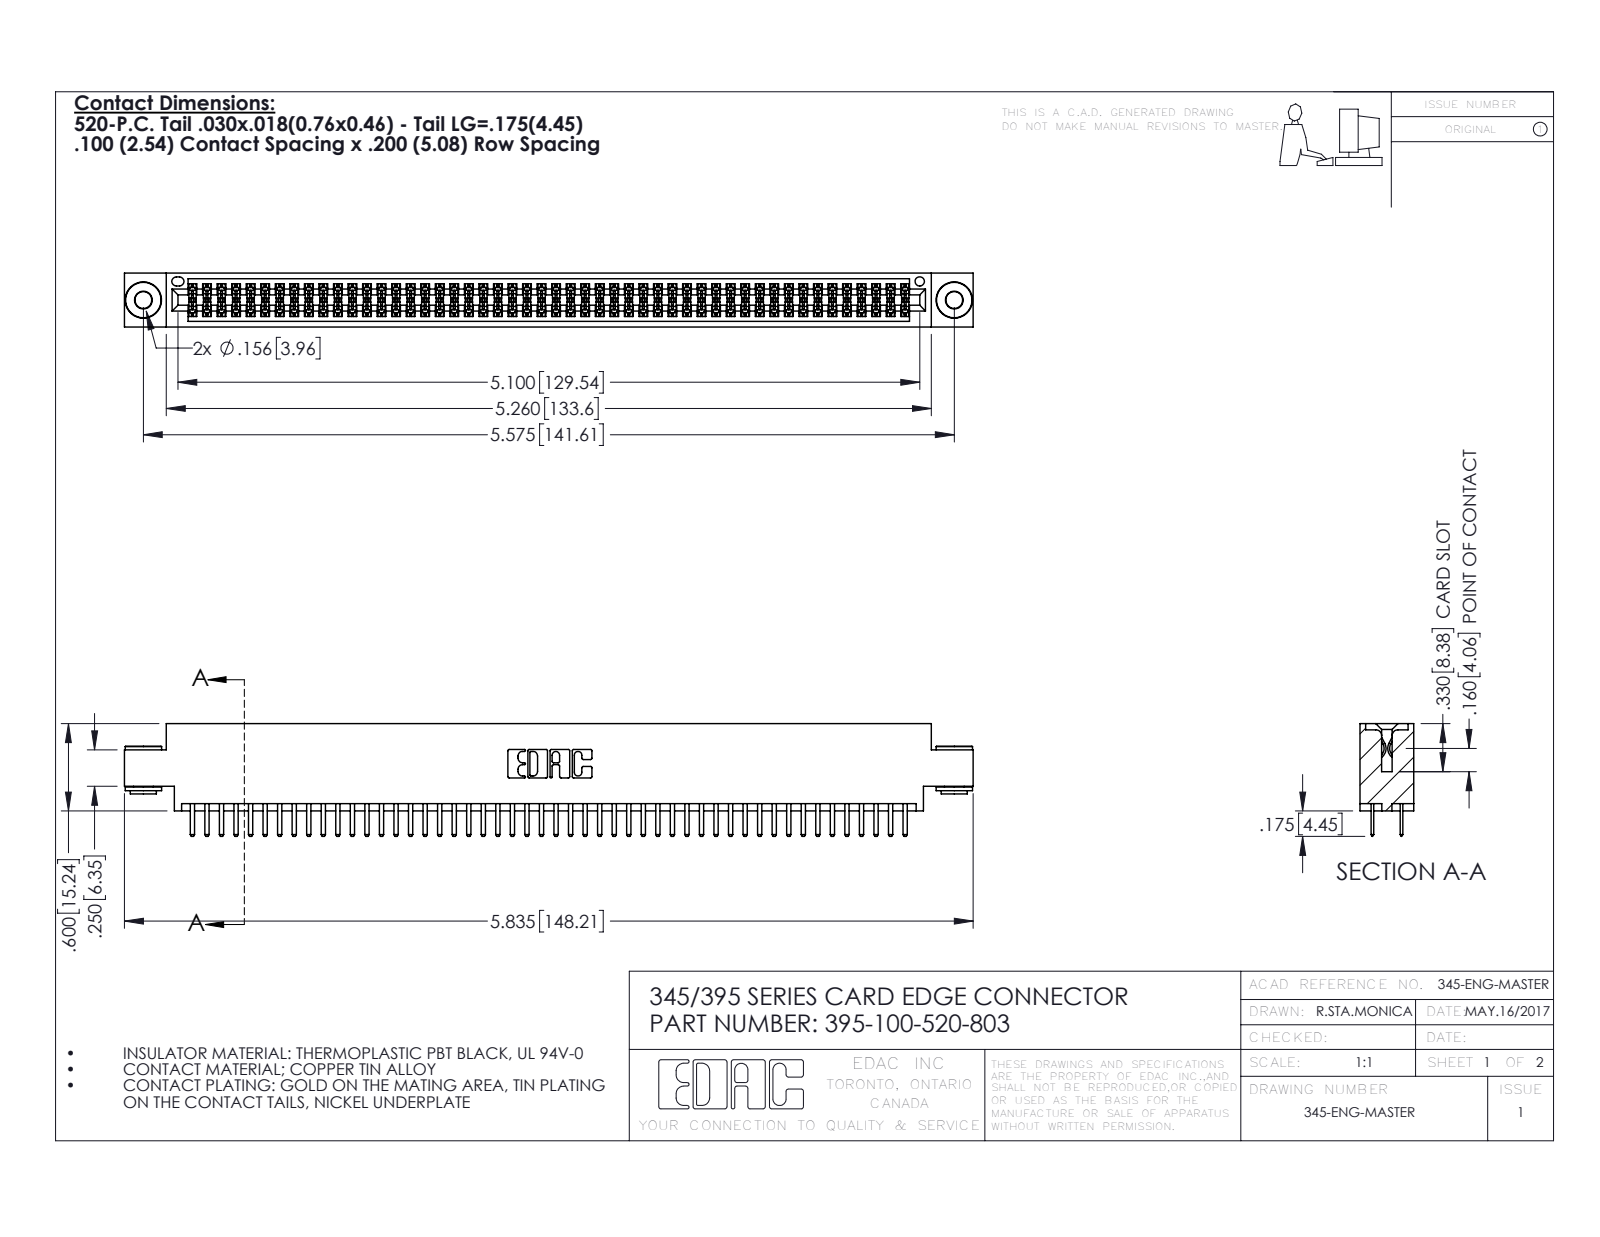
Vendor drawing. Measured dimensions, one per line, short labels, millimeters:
name: 345-292-001_345-293-120; 345 Part_0.170 Offset - 0.156 Dia-TH; 345-250-002_345-250-002-102; 395-100-520-803
written by: SolidWorks 2016 (CONFIG_CONTROL_DESIGN)
unit: mm
bodies: 103 solids, 5568 faces (3594 planar, 1966 cylindrical, 8 other)
size: 148.2 × 19.7 × 9.4
volume: 14 300 mm³; area: 21 600 mm²
holes: 2× ⌀2.9, 2× ⌀4, 1× ⌀1.6
bosses: 2× ⌀6.4, 2× ⌀4.6, 2× ⌀3.5
rounds: 150× R0.2, 104× R0.3, 22× R0.3, 6× R0.2, 6× R0.8, 3× R0.7, 2× R0.4, 2× R0.5
face distances: 1.8, 7.6, 5.1, 9.4, 2.5, 6.9, 0.6, 5.7, 0.6, 4.4
hole spacings: 6.9, 135.6, 141.6
